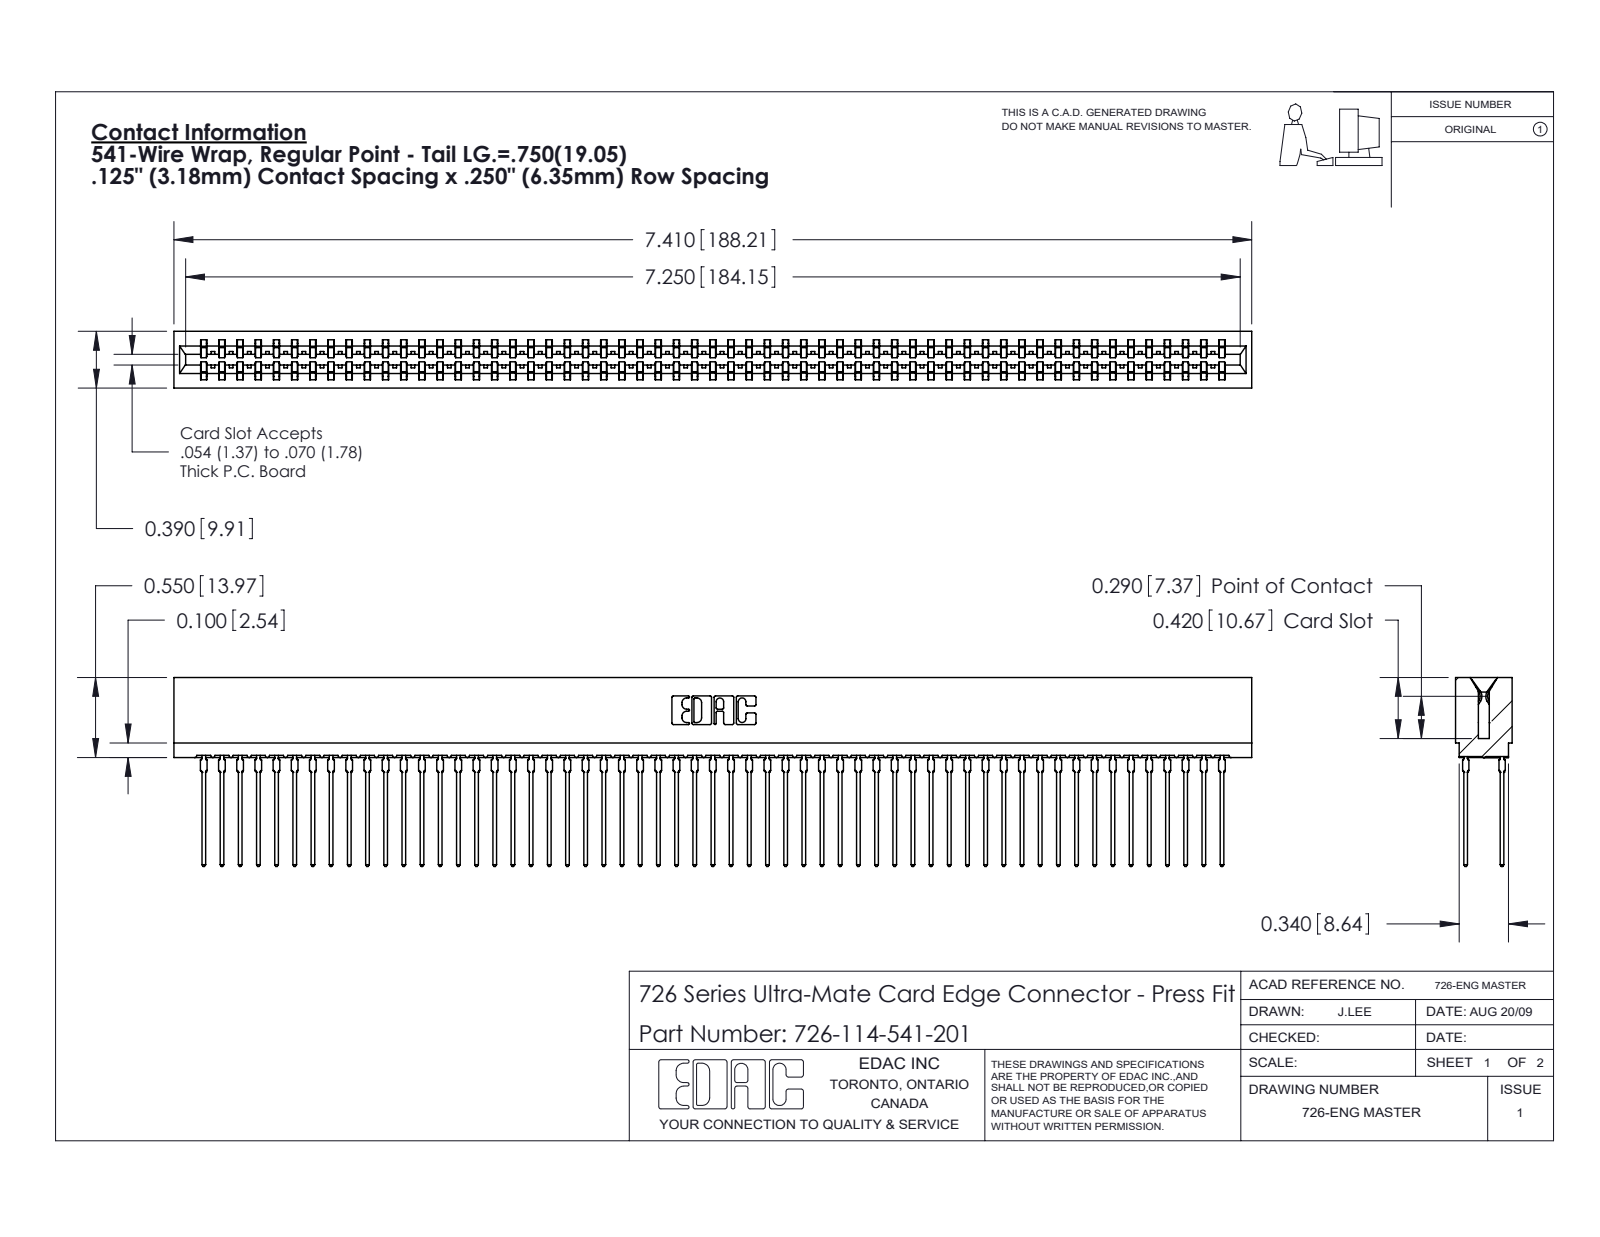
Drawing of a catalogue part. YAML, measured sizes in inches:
part_name: "726-114-541-201; 746-292-001_541; 726 Part_.515 Slot Depth - 01"
step_written_by: "SolidWorks 2020 (CONFIG_CONTROL_DESIGN)"
units: inches
bodies: {solids: 115, faces: 10300, planar: 5299, cylindrical: 2037, other: 2964}
overall_size: [7.41, 1.299, 0.39]
volume: 1.09
surface_area: 51.08
partial_cylinders:
  - {radius: 0.021, count: 228}
  - {radius: 0.015, count: 58}
  - {radius: 0.01, count: 22}
  - {radius: 0.005, count: 8}
  - {radius: 0.011, count: 8}
  - {radius: 0.007, count: 6}
  - {radius: 0.031, count: 6}
  - {radius: 0.026, count: 3}
face_to_face_distances: [0.057, 0.333, 0.025, 0.307, 0.25, 0.39, 0.083, 0.275, 0.225, 0.365]
